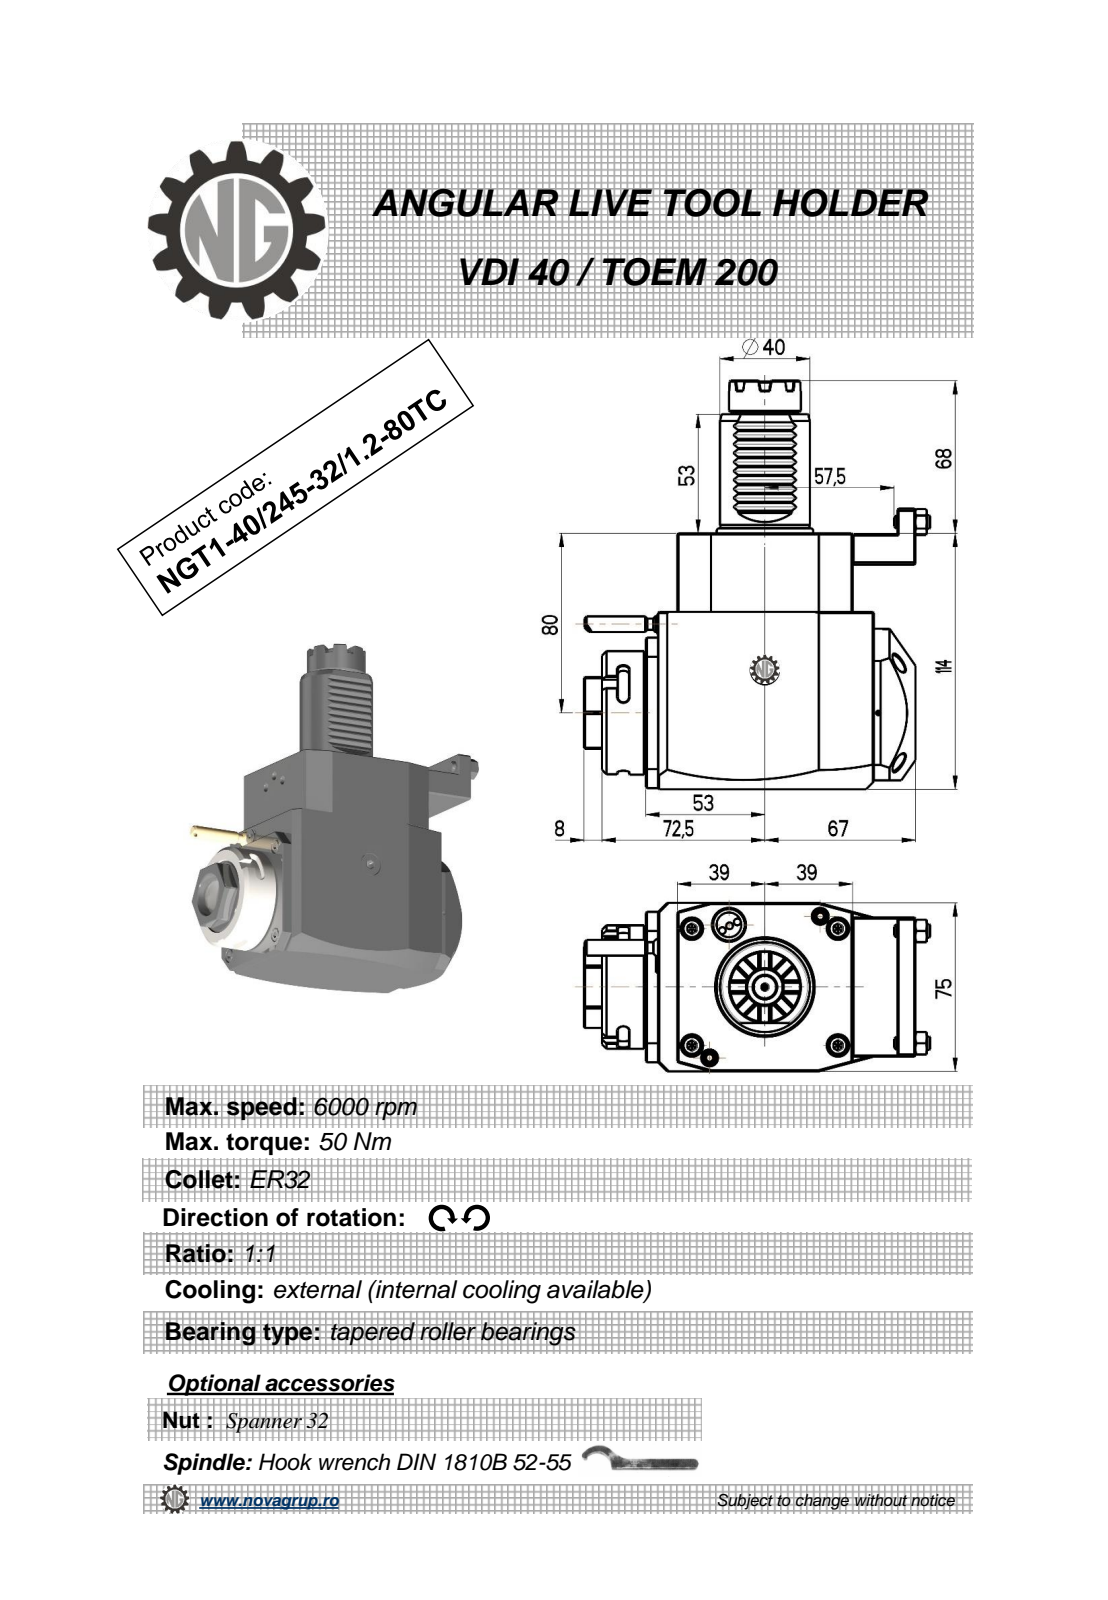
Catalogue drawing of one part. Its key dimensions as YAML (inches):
part_name: "NGT1_40_245_32_1_2_80TC"
step_written_by: "PRO/ENGINEER BY PARAMETRIC TECHNOLOGY CORPORATION, 2010280 (CONFIG_CONTROL_DESIGN)"
units: inches
bodies: {solids: 1, faces: 421, planar: 225, cylindrical: 66, other: 130}
overall_size: [7.165, 6.063, 2.953]
volume: 59.93
surface_area: 117.2
round_holes:
  - {diameter: 0.098, count: 1}
  - {diameter: 0.118, count: 1}
  - {diameter: 0.906, count: 1}
round_bosses_or_shafts:
  - {diameter: 0.236, count: 2}
  - {diameter: 2.165, count: 1}
  - {diameter: 1.89, count: 1}
  - {diameter: 1.575, count: 1}
  - {diameter: 1.26, count: 1}
  - {diameter: 0.677, count: 1}
  - {diameter: 0.315, count: 1}
  - {diameter: 0.276, count: 1}
partial_cylinders:
  - {radius: 0.012, count: 10}
  - {radius: 0.012, count: 10}
  - {radius: 0.098, count: 6}
  - {radius: 7.087, count: 2}
  - {radius: 0.02, count: 1}
  - {radius: 0.965, count: 1}
  - {radius: 1.476, count: 1}
face_to_face_distances: [2.953, 0.551, 4.488, 4.724, 4.173, 0.02, 5.492, 3.937, 0.768, 1.319]
hole_center_spacings: [1.701]
